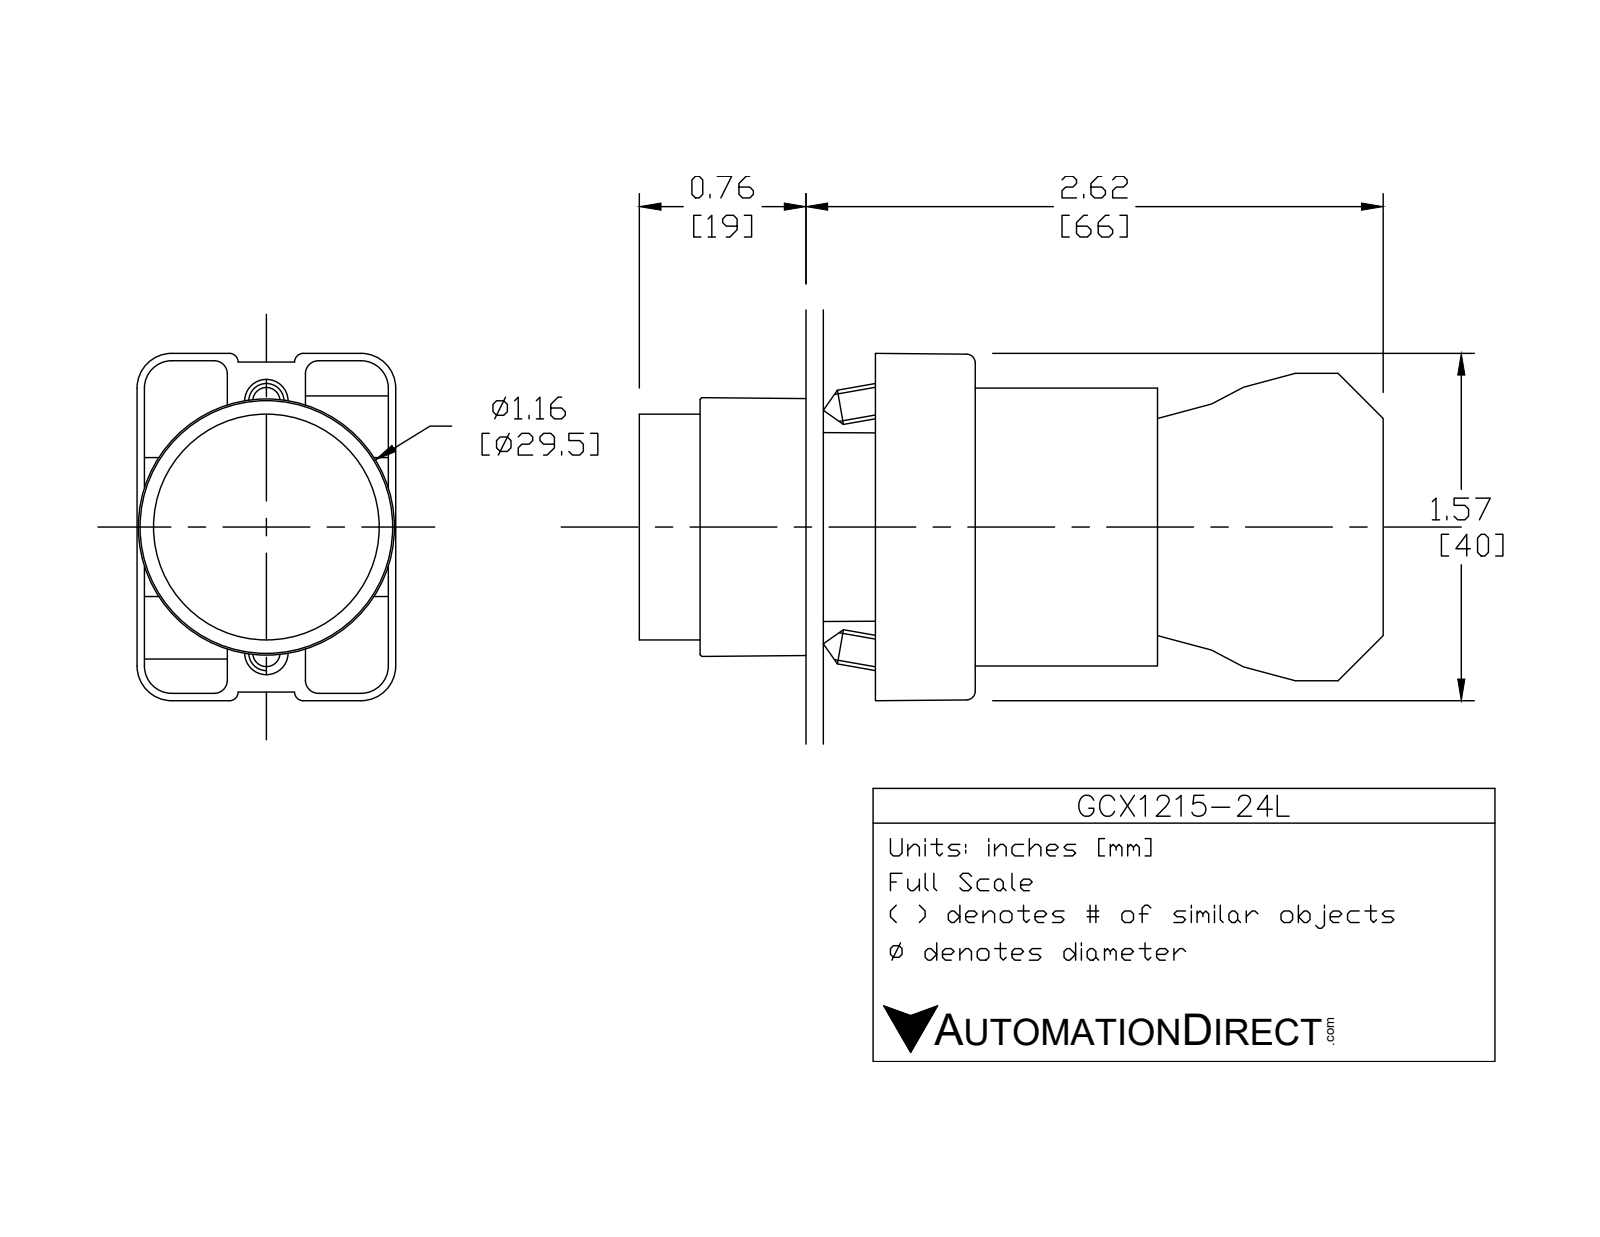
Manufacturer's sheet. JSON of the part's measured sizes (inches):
{"part_name": "ecx1040; ECX1050; GCX1215-24L; GCX1215L OPERATOR (+1 more)", "step_written_by": "SolidWorks 2016 (AUTOMOTIVE_DESIGN)", "units": "inches", "bodies": {"solids": 7, "faces": 425, "planar": 250, "cylindrical": 144, "other": 31}, "overall_size": [3.319, 1.581, 1.177], "volume_in3": 2.721, "surface_area_in2": 36.32, "round_holes": [[0.079, 2], [0.124, 2], [0.13, 2], [0.087, 1], [0.197, 1], [0.469, 1], [0.878, 1], [0.888, 1], [1.024, 1]], "round_bosses_or_shafts": [[0.157, 4], [1.175, 1], [1.004, 1], [0.945, 1], [0.856, 1], [0.78, 1], [0.504, 1]], "partial_cylinders_radius": [[0.059, 24], [0.041, 12], [0.124, 12], [0.157, 12], [0.039, 8], [0.128, 2], [0.02, 1], [0.063, 1]], "face_to_face_distances": [0.827, 0.579, 1.171, 2.02, 1.193, 0.031, 0.033, 0.573, 1.165, 0.593], "hole_center_spacings": [0.236, 0.544, 0.472, 0.49]}
